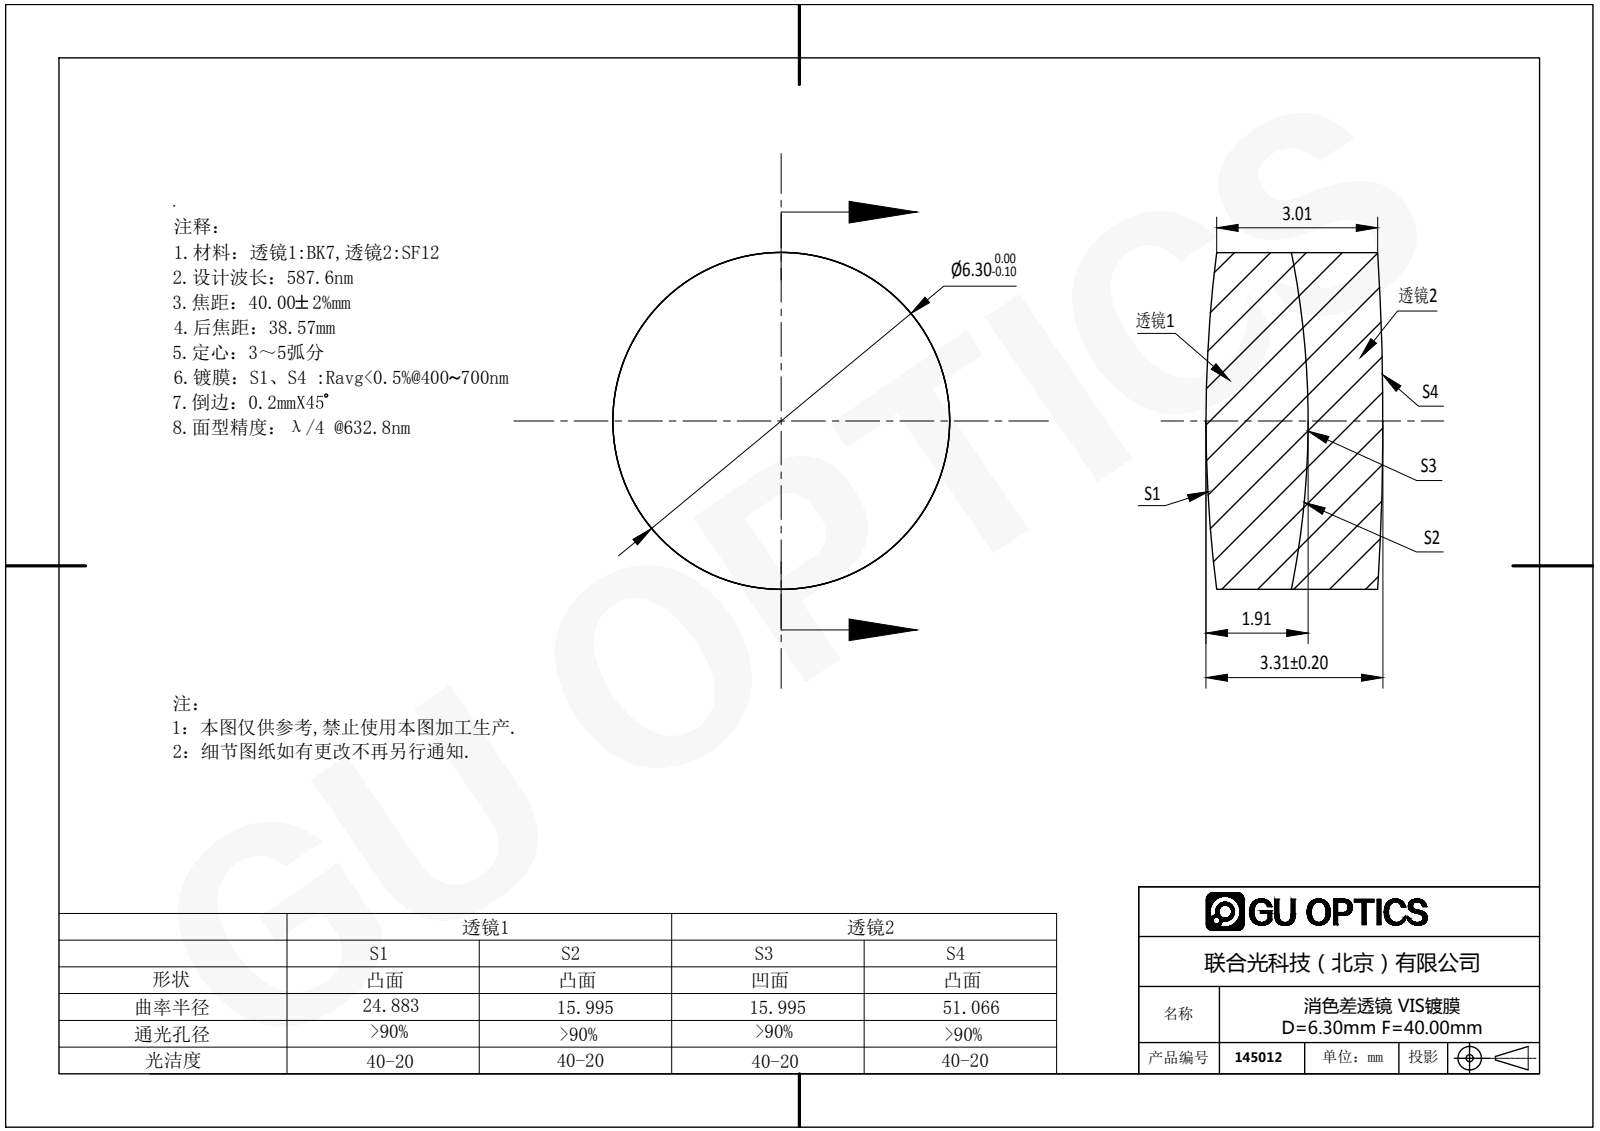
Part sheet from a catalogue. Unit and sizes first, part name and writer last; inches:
Units: inches
Overall size (bounding box): 0.248 × 0.248 × 0.13
Round bosses / shafts (diameter × count): ⌀0.248 ×1
Volume: 0.006 in³ · Surface area: 0.287 in²
Bodies: 2 solids, 12 faces (0 planar, 4 cylindrical, 8 other)
Part name (STEP PRODUCT): 145012
STEP written by: SolidWorks 2016 (AUTOMOTIVE_DESIGN)
